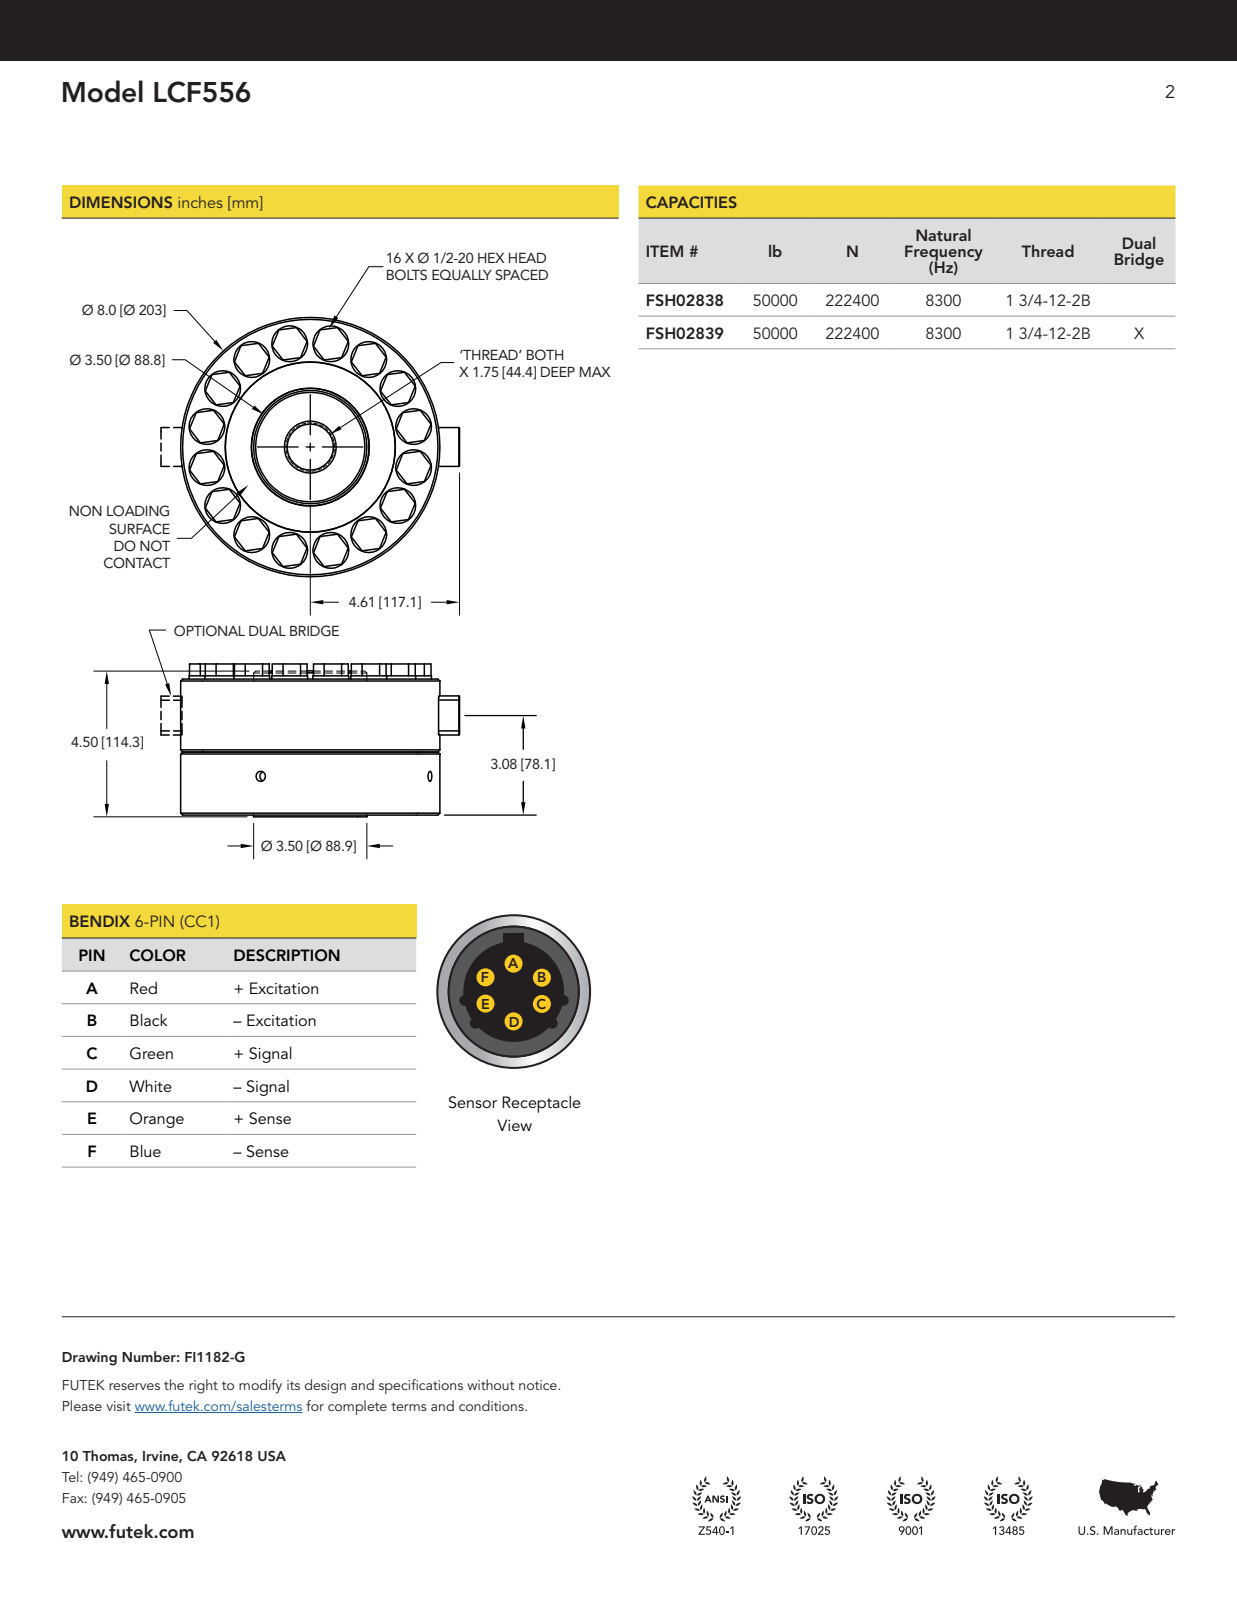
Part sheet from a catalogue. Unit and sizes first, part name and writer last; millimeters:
Units: millimetres
Overall size (bounding box): 217.9 × 203.2 × 117.2
Round holes (diameter × count): ⌀11.6 ×16, ⌀3.2 ×5, ⌀2.3 ×4, ⌀7.9 ×4, ⌀3.3 ×3, ⌀1.5 ×1, ⌀4.7 ×1, ⌀14 ×1, ⌀15.9 ×1, ⌀17.5 ×1, ⌀36.1 ×1, ⌀48.8 ×1
Round bosses / shafts (diameter × count): ⌀15.9 ×16, ⌀1.5 ×12, ⌀4.6 ×4, ⌀2.8 ×4, ⌀203.2 ×1, ⌀143 ×1, ⌀133.2 ×1, ⌀88.9 ×1
Partial cylindrical surfaces — rounded edges, fillets, slot ends (radius × count): R1.3 ×4, R1.6 ×4, R3.2 ×4
Main face-to-face distances: 0.8, 48.8, 1.5, 106.7, 57.9, 56.4, 49.5, 57.2, 50.3, 115.9
Hole centre spacings: 63.2, 152.5, 161.9, 32.2, 137.3, 82.6, 91.7, 91.7
Volume: 3 350 000 mm³ · Surface area: 227 700 mm²
Bodies: 1 solid, 400 faces (238 planar, 108 cylindrical, 54 other)
Part name (STEP PRODUCT): LCF555; ~PART1
STEP written by: Autodesk Inventor 2008 (AUTOMOTIVE_DESIGN)
